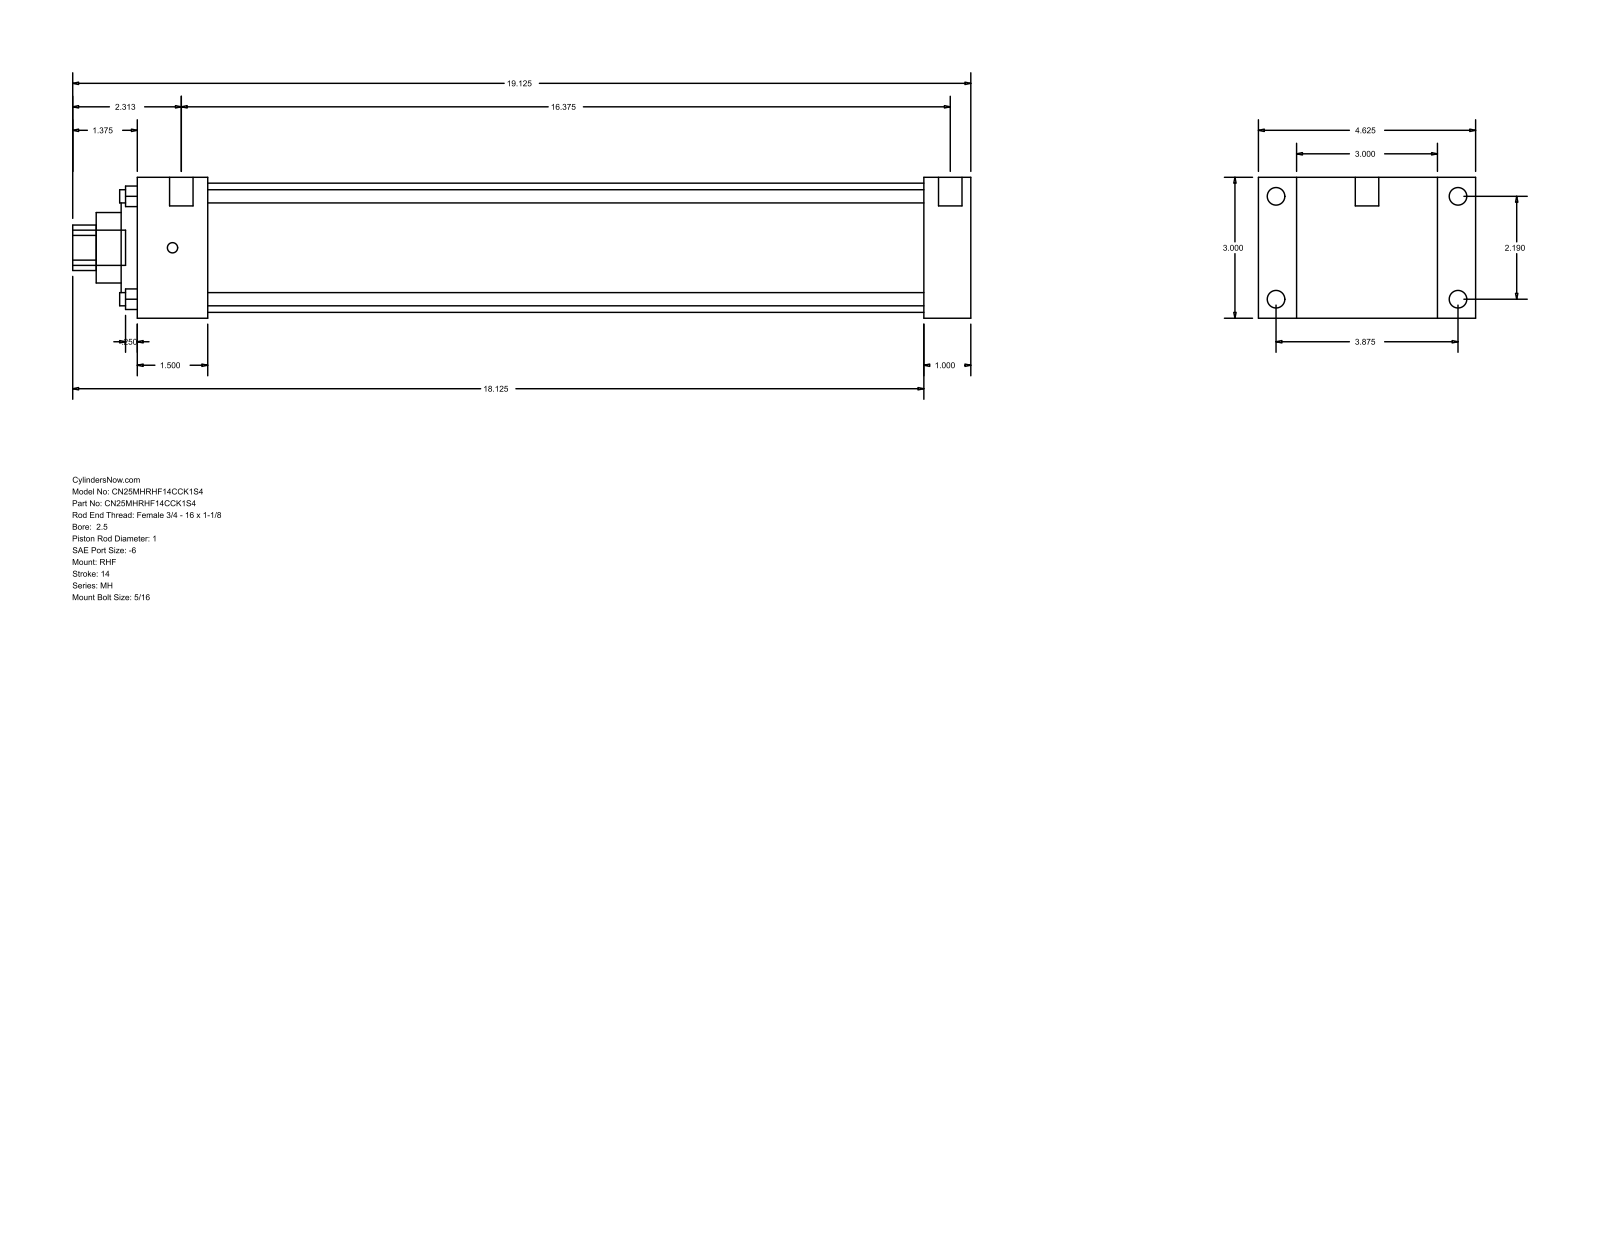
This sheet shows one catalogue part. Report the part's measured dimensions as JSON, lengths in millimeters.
{"part_name": "MH_RHF__0250_1", "step_written_by": "GSSL Pune (CONFIG_CONTROL_DESIGN)", "units": "millimeters", "bodies": {"solids": 0, "faces": 90, "planar": 61, "cylindrical": 29, "other": 0}, "overall_size": [485.77, 117.47, 76.2], "round_holes": [[7.14, 4], [25.4, 1], [38.1, 1], [60.33, 1], [69.85, 1]], "round_bosses_or_shafts": [[9.53, 4], [5.56, 4], [12.7, 2], [19.05, 1]], "partial_cylinders_radius": [[12.29, 1]], "face_to_face_distances": [76.2, 25.39, 20.64, 96.84, 450.85, 425.46, 117.48, 38.11, 387.35, 412.74], "hole_center_spacings": [39.33, 55.62, 78.66]}
